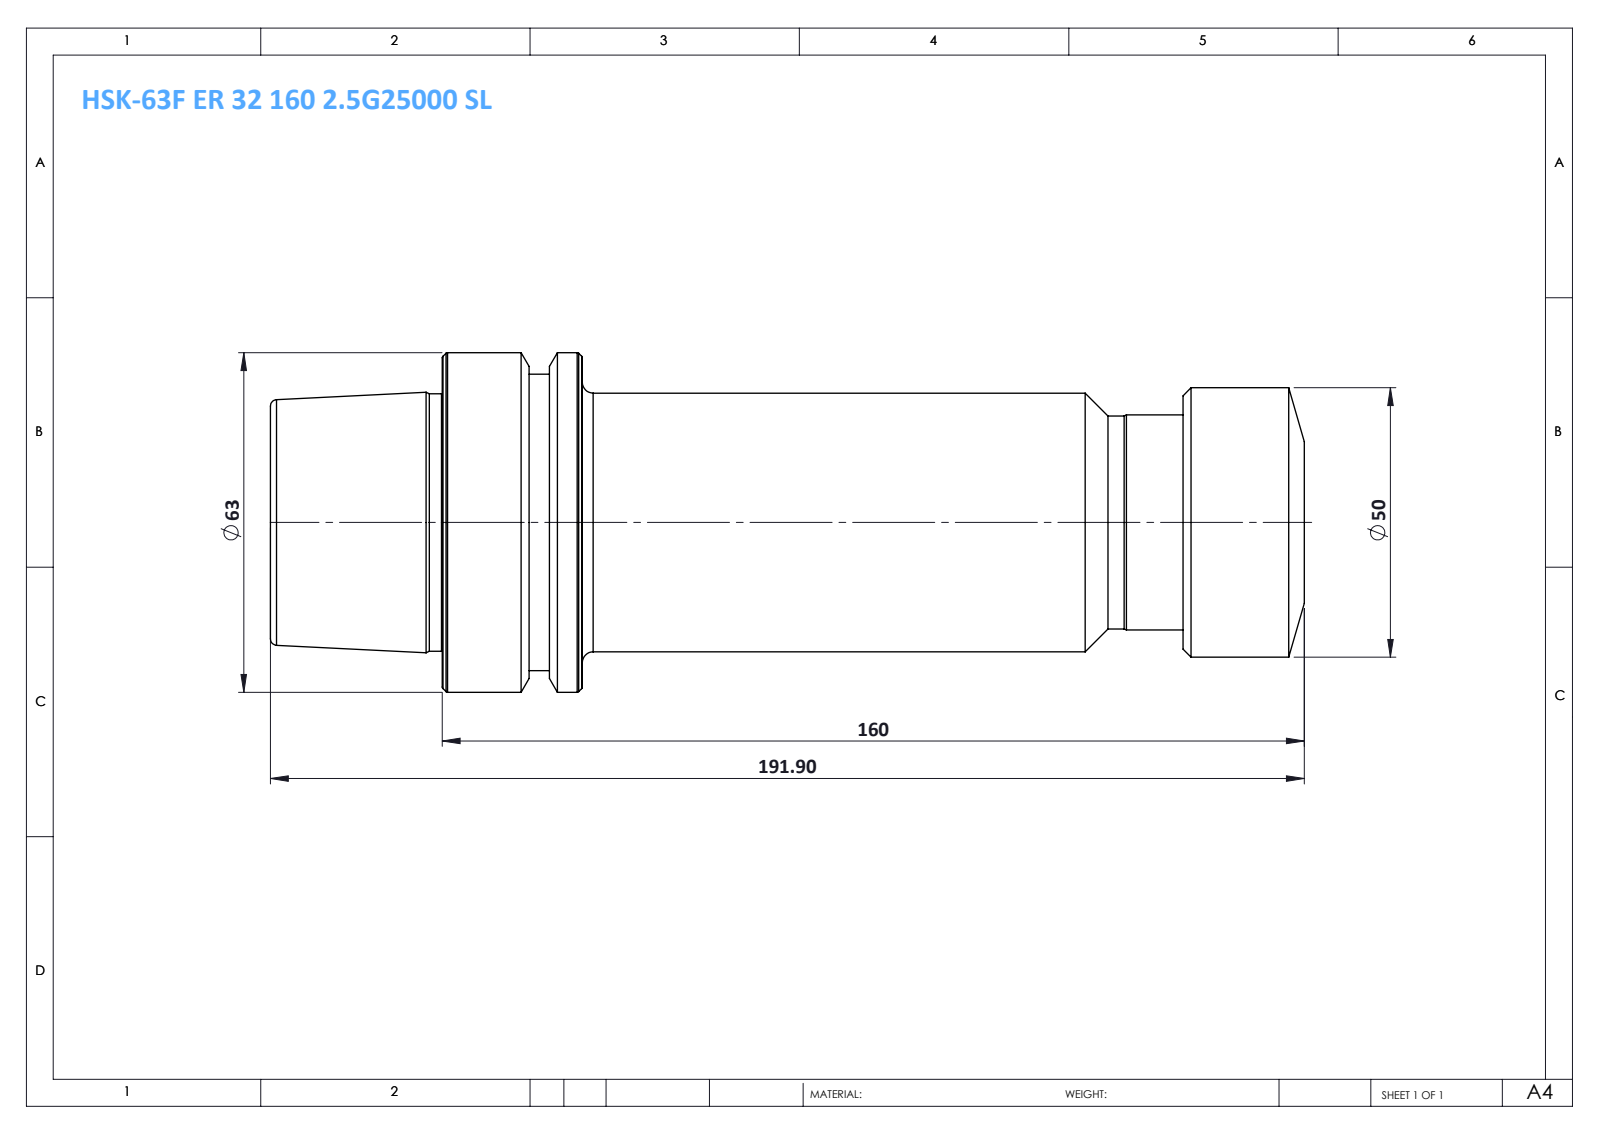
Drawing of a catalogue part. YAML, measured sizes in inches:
part_name: "HSK-A 63 ER 32 160 6.3G 20000 SL"
step_written_by: "SolidWorks 2014 (CONFIG_CONTROL_DESIGN)"
units: inches
bodies: {solids: 1, faces: 59, planar: 7, cylindrical: 16, other: 36}
overall_size: [7.555, 2.48, 2.48]
volume: 22.42
surface_area: 57.39
round_bosses_or_shafts:
  - {diameter: 2.48, count: 1}
  - {diameter: 2.165, count: 1}
  - {diameter: 1.969, count: 1}
  - {diameter: 1.89, count: 1}
  - {diameter: 1.881, count: 1}
  - {diameter: 1.571, count: 1}
  - {diameter: 1.555, count: 1}
face_to_face_distances: [2.28, 1.024, 1.256, 5.276, 6.299, 7.555, 0.886, 4.39, 5.413, 6.669]
